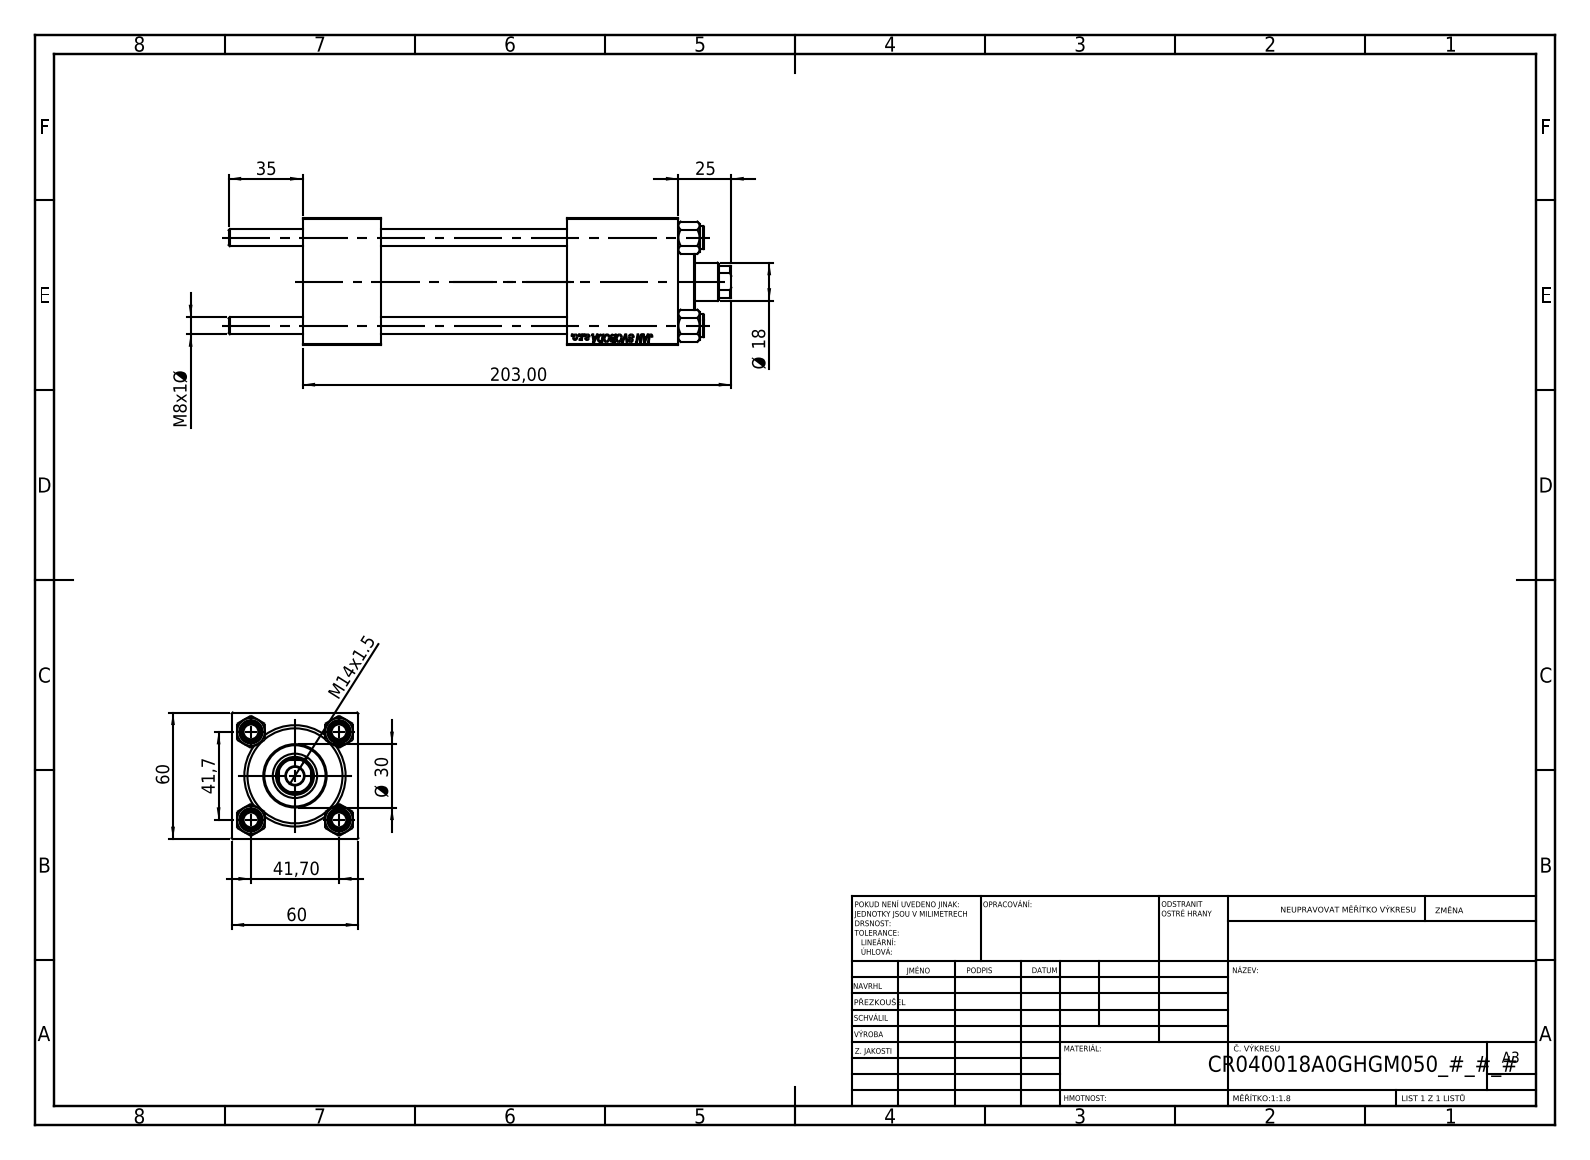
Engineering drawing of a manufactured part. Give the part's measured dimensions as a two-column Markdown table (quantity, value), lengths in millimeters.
| quantity | value |
| --- | --- |
| part name | V215CR_BODY_A; V215CR_VCP; NUT_M5; V215_VC_A (+1 more) |
| STEP written by | SolidWorks 2019 (CONFIG_CONTROL_DESIGN) |
| units | millimeters |
| bodies | 11 solids, 1135 faces (521 planar, 78 cylindrical, 536 other) |
| overall size | 238 × 60 × 60 |
| volume | 439 723 mm³ |
| surface area | 126 824 mm² |
| round holes (diameter × count) | 8 × 4, 7 × 2, 16.66 × 2, 24 × 2, 8.5 × 1, 18 × 1, 21 × 1, 31 × 1, 40 × 1, 45 × 1 |
| round bosses / shafts (diameter × count) | 11 × 4, 46 × 1, 30 × 1 |
| partial cylindrical surfaces (radius × count) | 8.5 × 1 |
| main face-to-face distances | 60, 37, 178, 141, 53, 125, 88, 149.3, 112.3, 24.3 |
| hole center spacings | 29.49, 41.7, 58.97, 122.5 |
